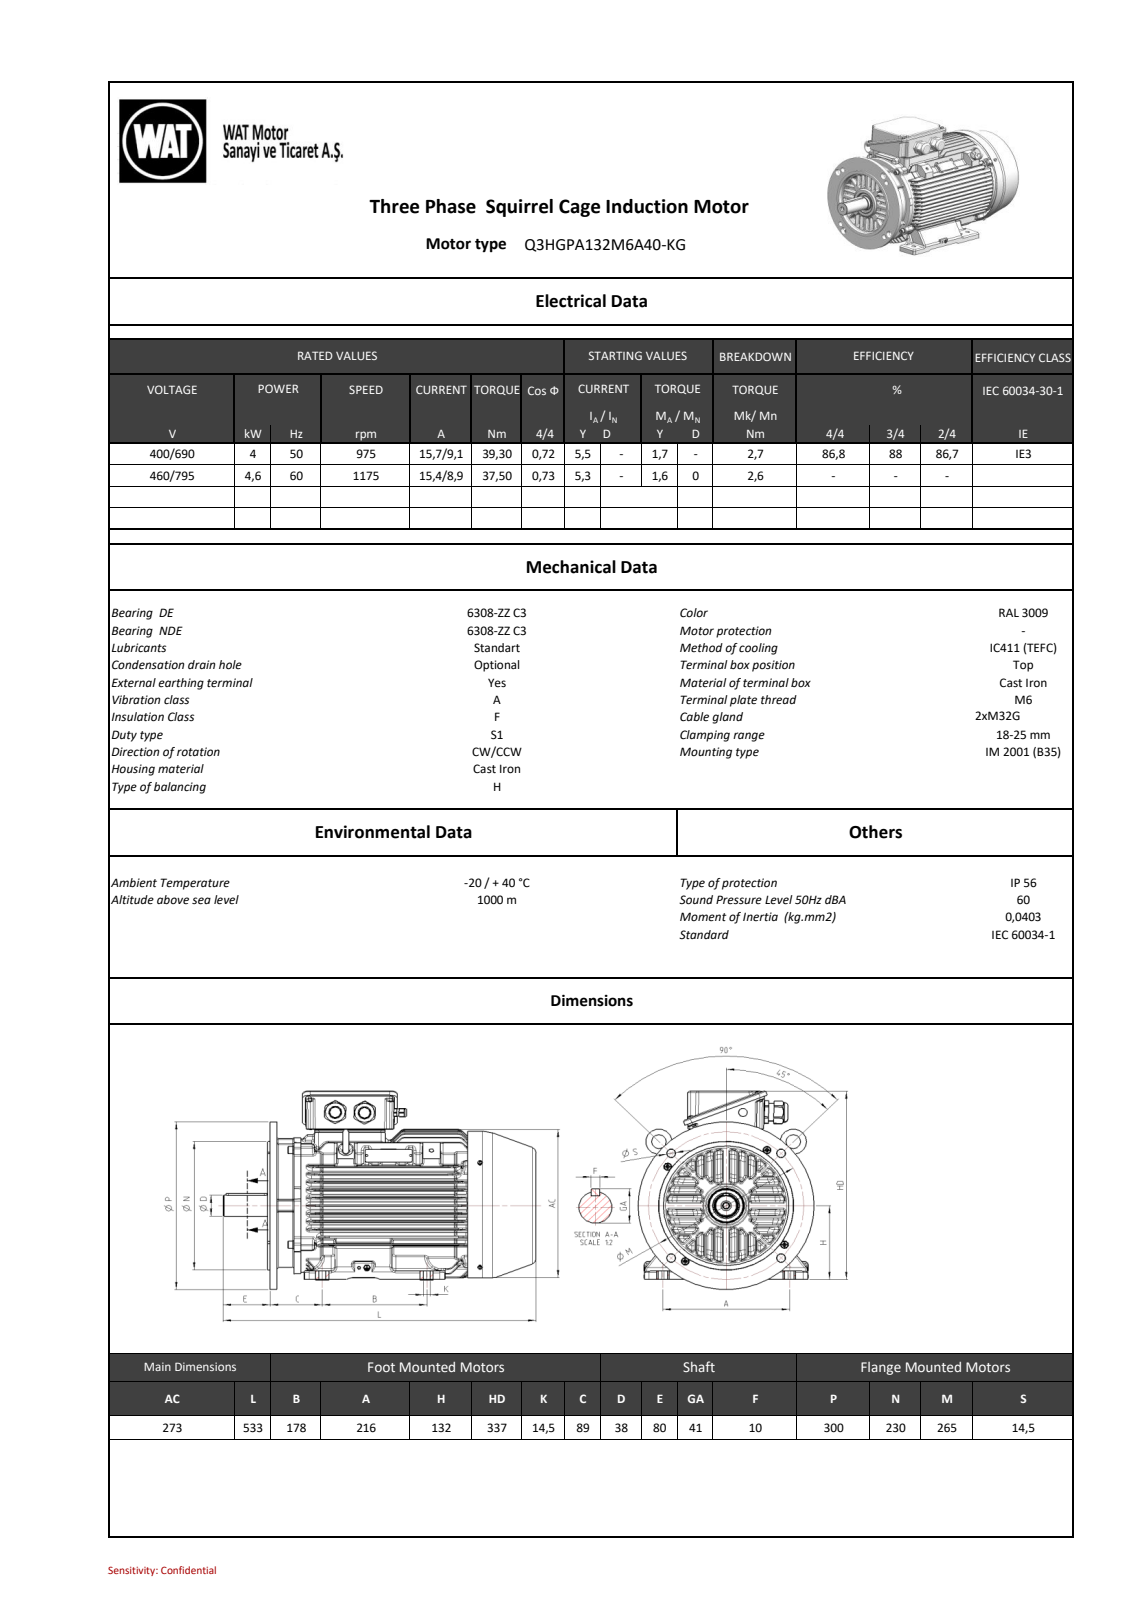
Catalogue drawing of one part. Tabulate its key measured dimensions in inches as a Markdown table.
| quantity | value |
| --- | --- |
| part name | 26000A30F4D8ro8y |
| STEP written by | SIEMENS PLM Software NX 11.0 (AUTOMOTIVE_DESIGN) |
| units | inches |
| bodies | 0 solids, 6334 faces (1126 planar, 1750 cylindrical, 3458 other) |
| overall size | 20.984 × 13.993 × 11.811 |
| round holes (diameter × count) | 0.217 × 8, 0.268 × 8, 0.335 × 4, 0.63 × 4, 0.098 × 2, 0.165 × 2, 0.748 × 2, 0.827 × 2, 0.197 × 1, 0.406 × 1, 0.512 × 1, 1.346 × 1 |
| round bosses / shafts (diameter × count) | 0.512 × 4, 0.341 × 4, 0.315 × 4, 1.417 × 2, 1.358 × 2, 1.23 × 2, 11.811 × 1, 10.512 × 1 |
| partial cylindrical surfaces (radius × count) | 0.157 × 299, 0.118 × 175, 0.059 × 106, 0.079 × 84, 0.071 × 64, 0.236 × 32, 1.102 × 24, 1.378 × 24 |
| main face-to-face distances | 0.542, 2.202, 0.544, 1.086, 4.338, 0.472, 3.252, 3.793, 0.547, 1.092 |
| hole center spacings | 5.354, 4.783, 6.765, 4.851, 7.225, 1.661, 4.851, 5.487 |
